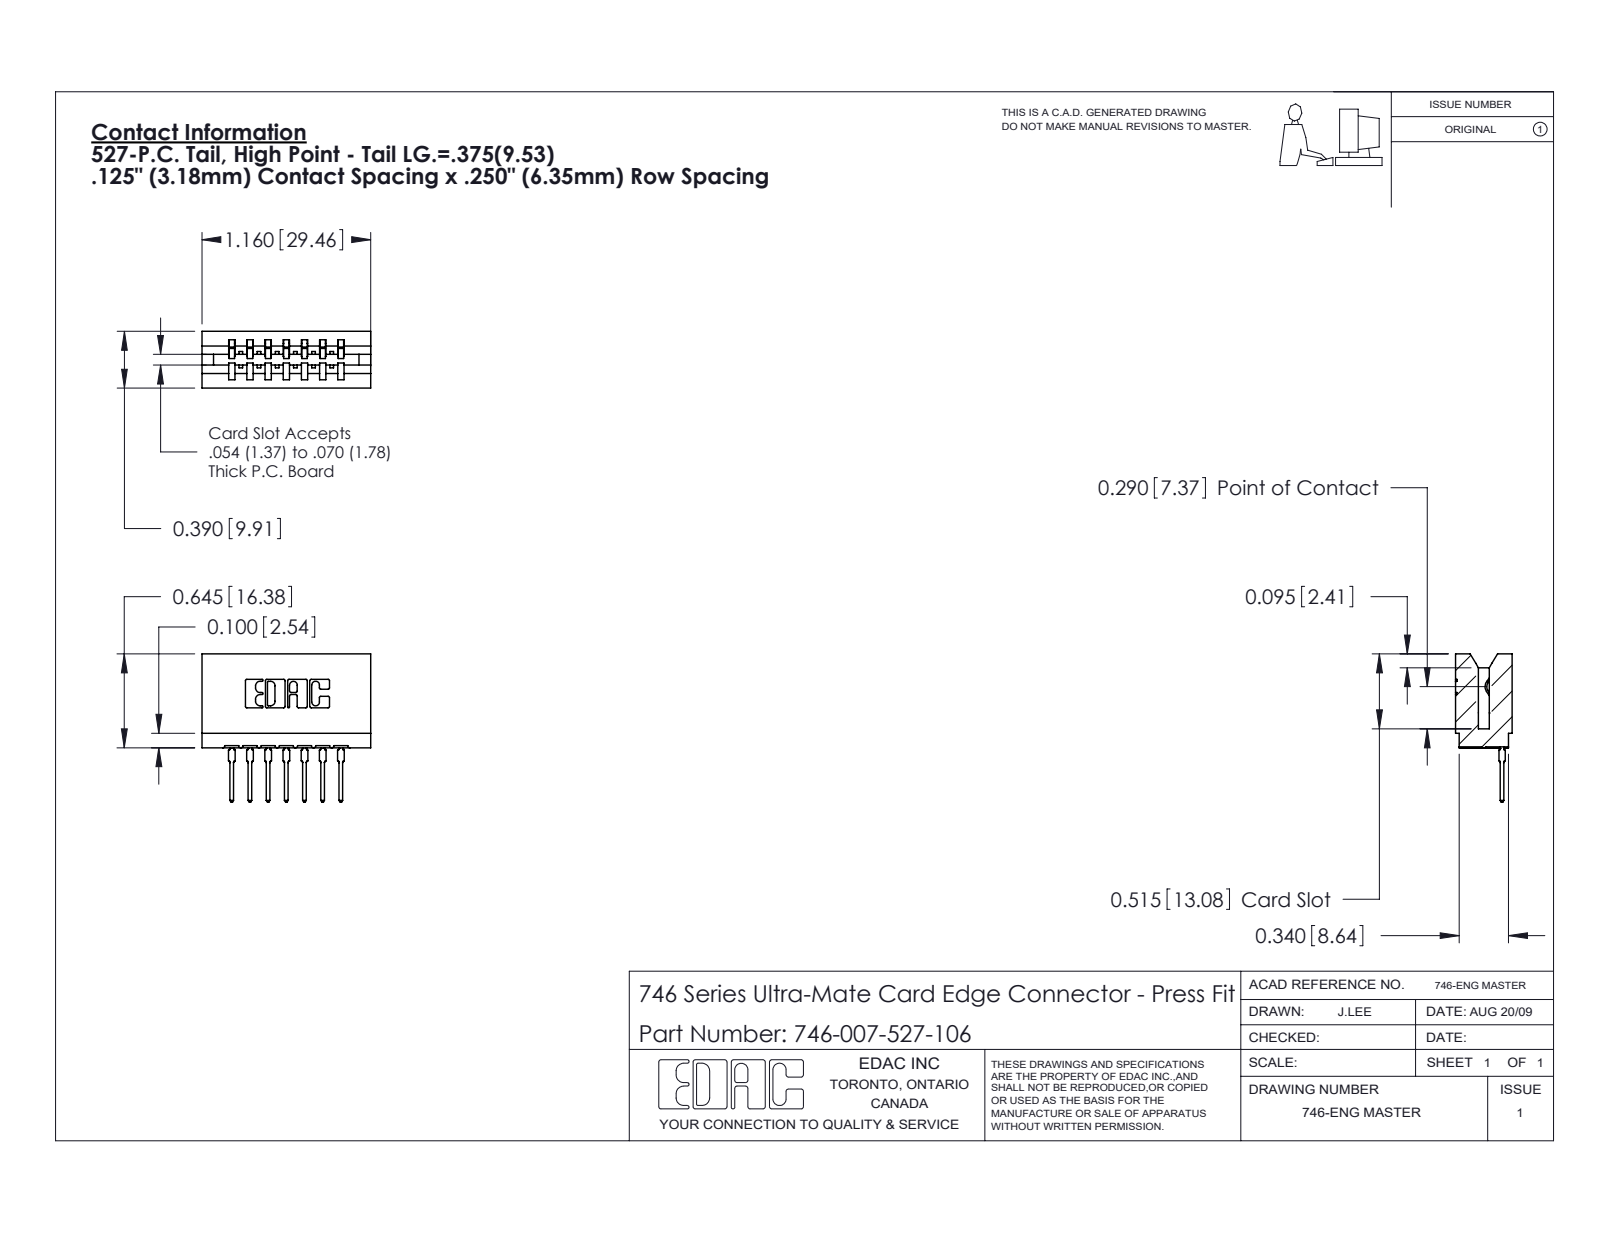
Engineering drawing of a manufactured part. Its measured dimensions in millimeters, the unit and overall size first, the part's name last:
Units: millimetres
Overall size (bounding box): 29.5 × 25.9 × 9.9
Partial cylindrical surfaces — rounded edges, fillets, slot ends (radius × count): R0.3 ×22, R0.5 ×14, R0.4 ×8, R0.2 ×6, R0.8 ×6, R0.1 ×4, R0.3 ×4, R0.7 ×3
Main face-to-face distances: 6.4, 1.1, 8.5, 12.7, 3.2, 3.2, 1.4, 5.3, 7.4, 9.9
Volume: 3 310 mm³ · Surface area: 4 359 mm²
Bodies: 8 solids, 854 faces (497 planar, 175 cylindrical, 182 other)
Part name (STEP PRODUCT): 746 Part_.515 Slot Depth - 06; 746-292-001_527; 746-007-527-106
STEP written by: SolidWorks 2020 (CONFIG_CONTROL_DESIGN)
